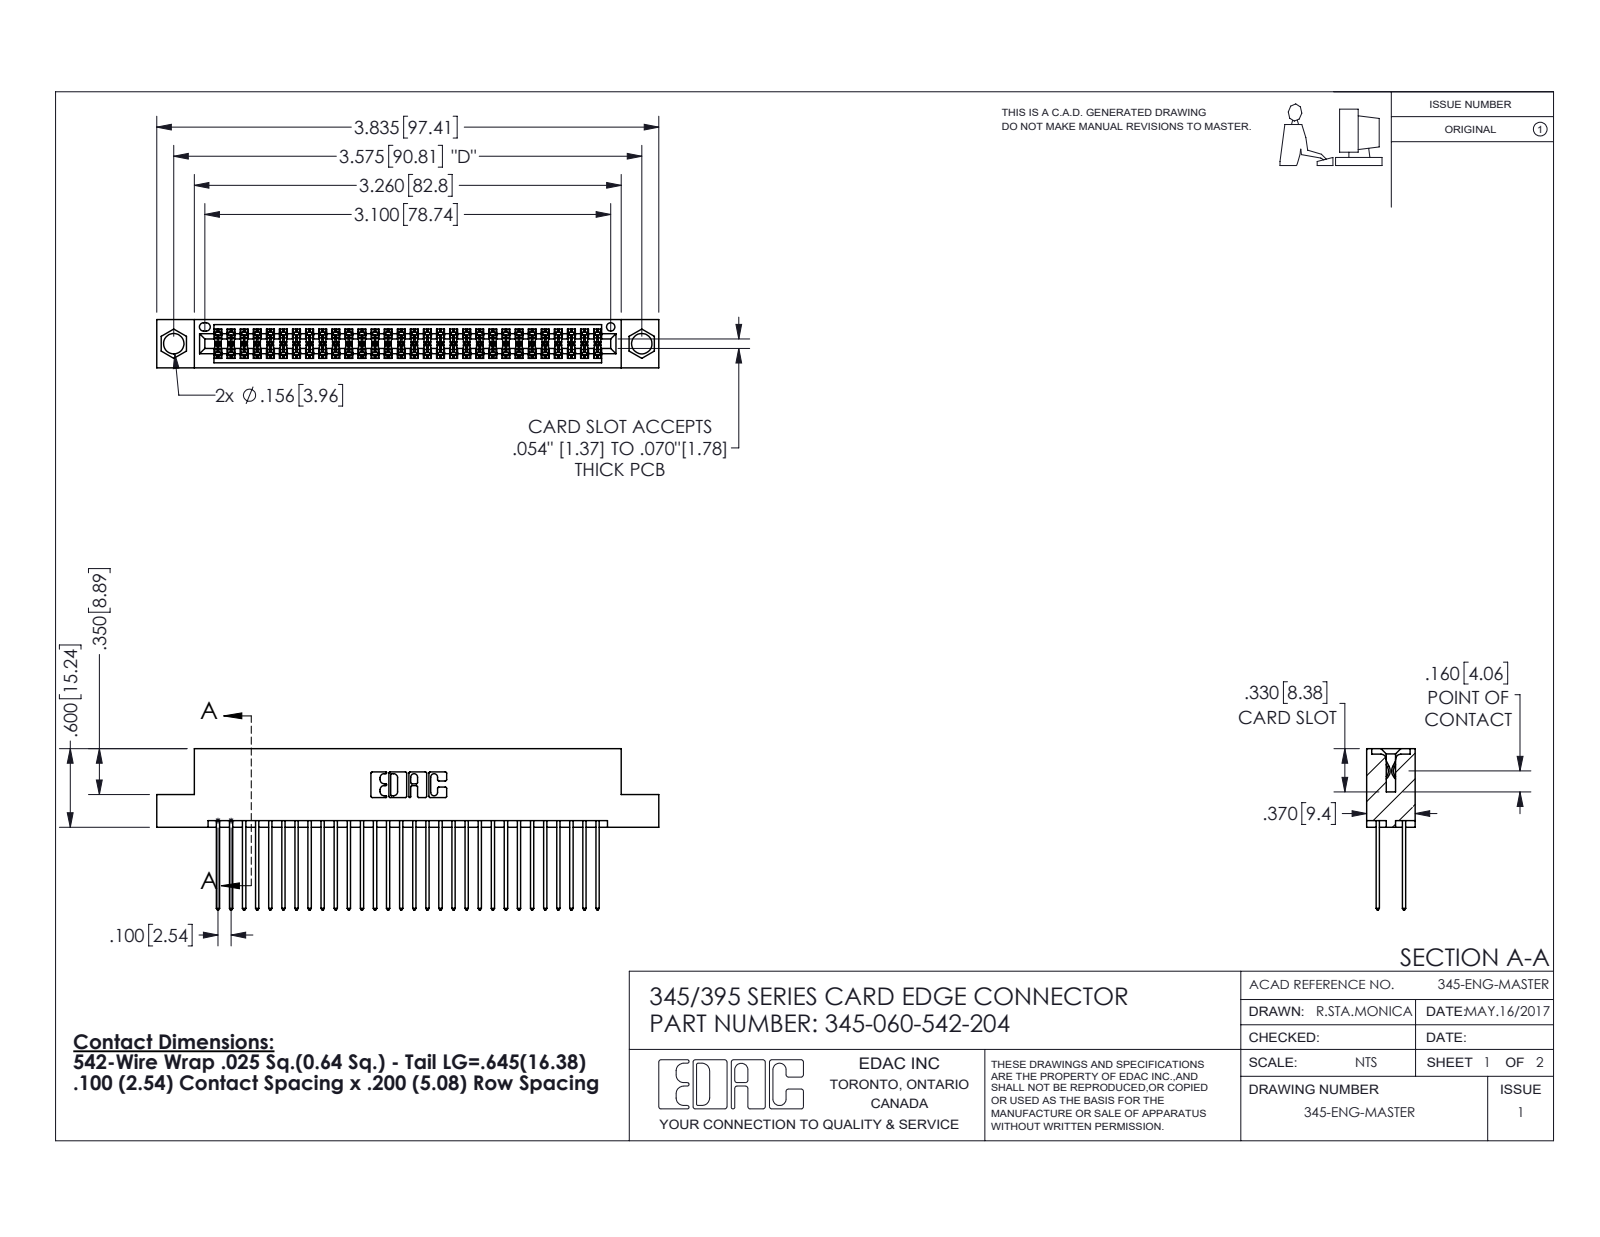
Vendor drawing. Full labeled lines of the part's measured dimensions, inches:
Part name (STEP PRODUCT): 345 Part_Flush Mounting Lugs - 0.156 Dia-TI; 345-292-001_345-293-142; 345-060-542-204
STEP written by: SolidWorks 2020 (CONFIG_CONTROL_DESIGN)
Units: inches
Bodies: 61 solids, 3140 faces (2074 planar, 1066 cylindrical, 0 other)
Overall size (bounding box): 3.835 × 1.232 × 0.37
Volume: 0.581 in³ · Surface area: 23.26 in²
Round holes (diameter × count): ⌀0.156 ×2, ⌀0.064 ×1
Partial cylindrical surfaces — rounded edges, fillets, slot ends (radius × count): R0.006 ×91, R0.01 ×60, R0.01 ×22, R0.007 ×6, R0.031 ×6, R0.026 ×3, R0.014 ×2, R0.019 ×2
Main face-to-face distances: 0.298, 0.072, 0.2, 0.098, 0.272, 0.025, 0.37, 0.225, 0.175, 0.149
Hole centre spacings: 0.27, 3.34, 3.575
